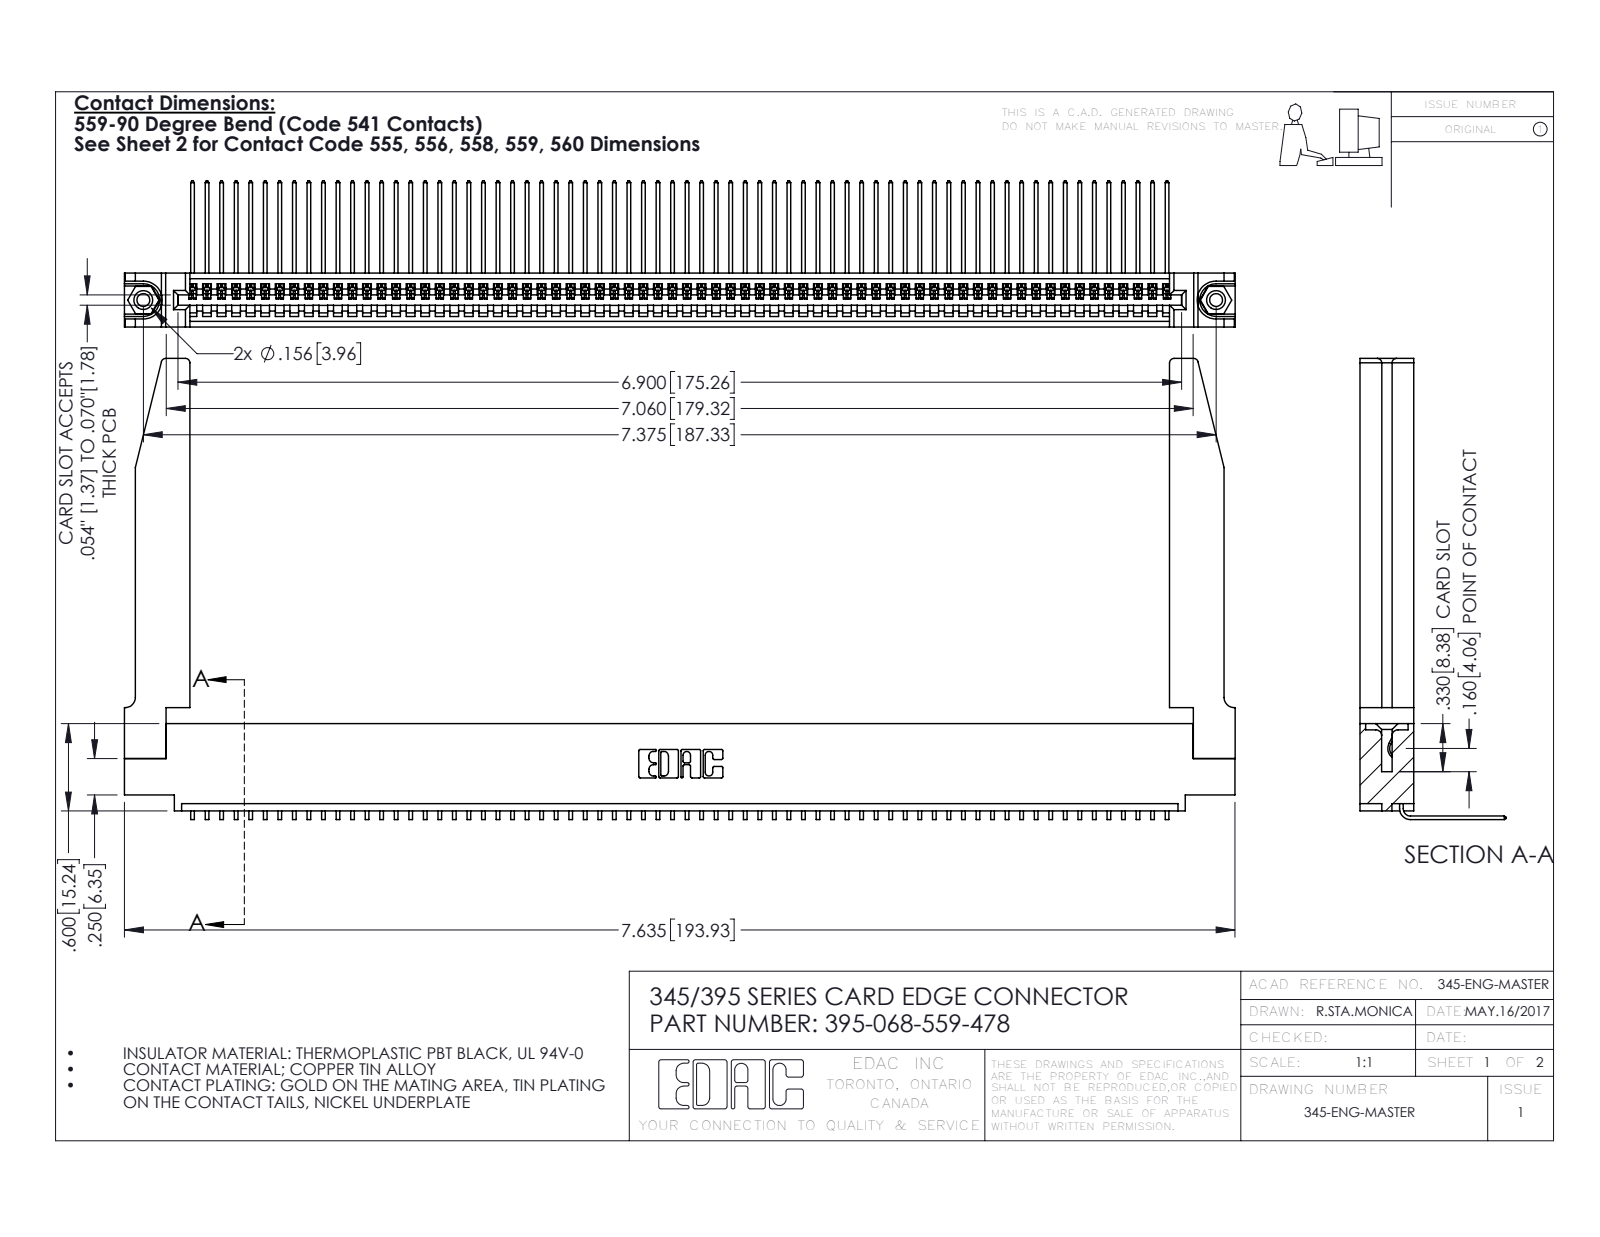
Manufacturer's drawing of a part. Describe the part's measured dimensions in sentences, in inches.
The part is named "345-292-001_558 559 Tail - 1; 395-068-559-478; 345-250-001_345-250-001-102; 345-220-078_345-220-078 (+1 more)". Its 3-D file was written by "SolidWorks 2016 (CONFIG_CONTROL_DESIGN)". It is 73 solids with 4444 faces: 3082 planar, 1310 cylindrical and 52 other. Overall it measures 7.636 by 3.169 by 1.005 inches. Its volume is 1.621 cubic inches and its surface area 52.05 square inches. Round holes: 2 of diameter 0.089, 2 of diameter 0.125, 2 of diameter 0.156, 1 of diameter 0.064. Round bosses or shafts: 2 of diameter 0.155. Partial cylindrical surfaces (rounded edges, fillets, slot ends): 136 of radius 0.006, 22 of radius 0.01, 8 of radius 0.03, 6 of radius 0.007, 6 of radius 0.031, 3 of radius 0.026, 2 of radius 0.031, 2 of radius 0.04. The main face-to-face distances are 0.072, 0.37, 0.298, 0.098, 0.272, 0.025, 0.2, 0.225, 0.149, 0.148. The hole center spacings are 0.27, 7.139, 7.375.
